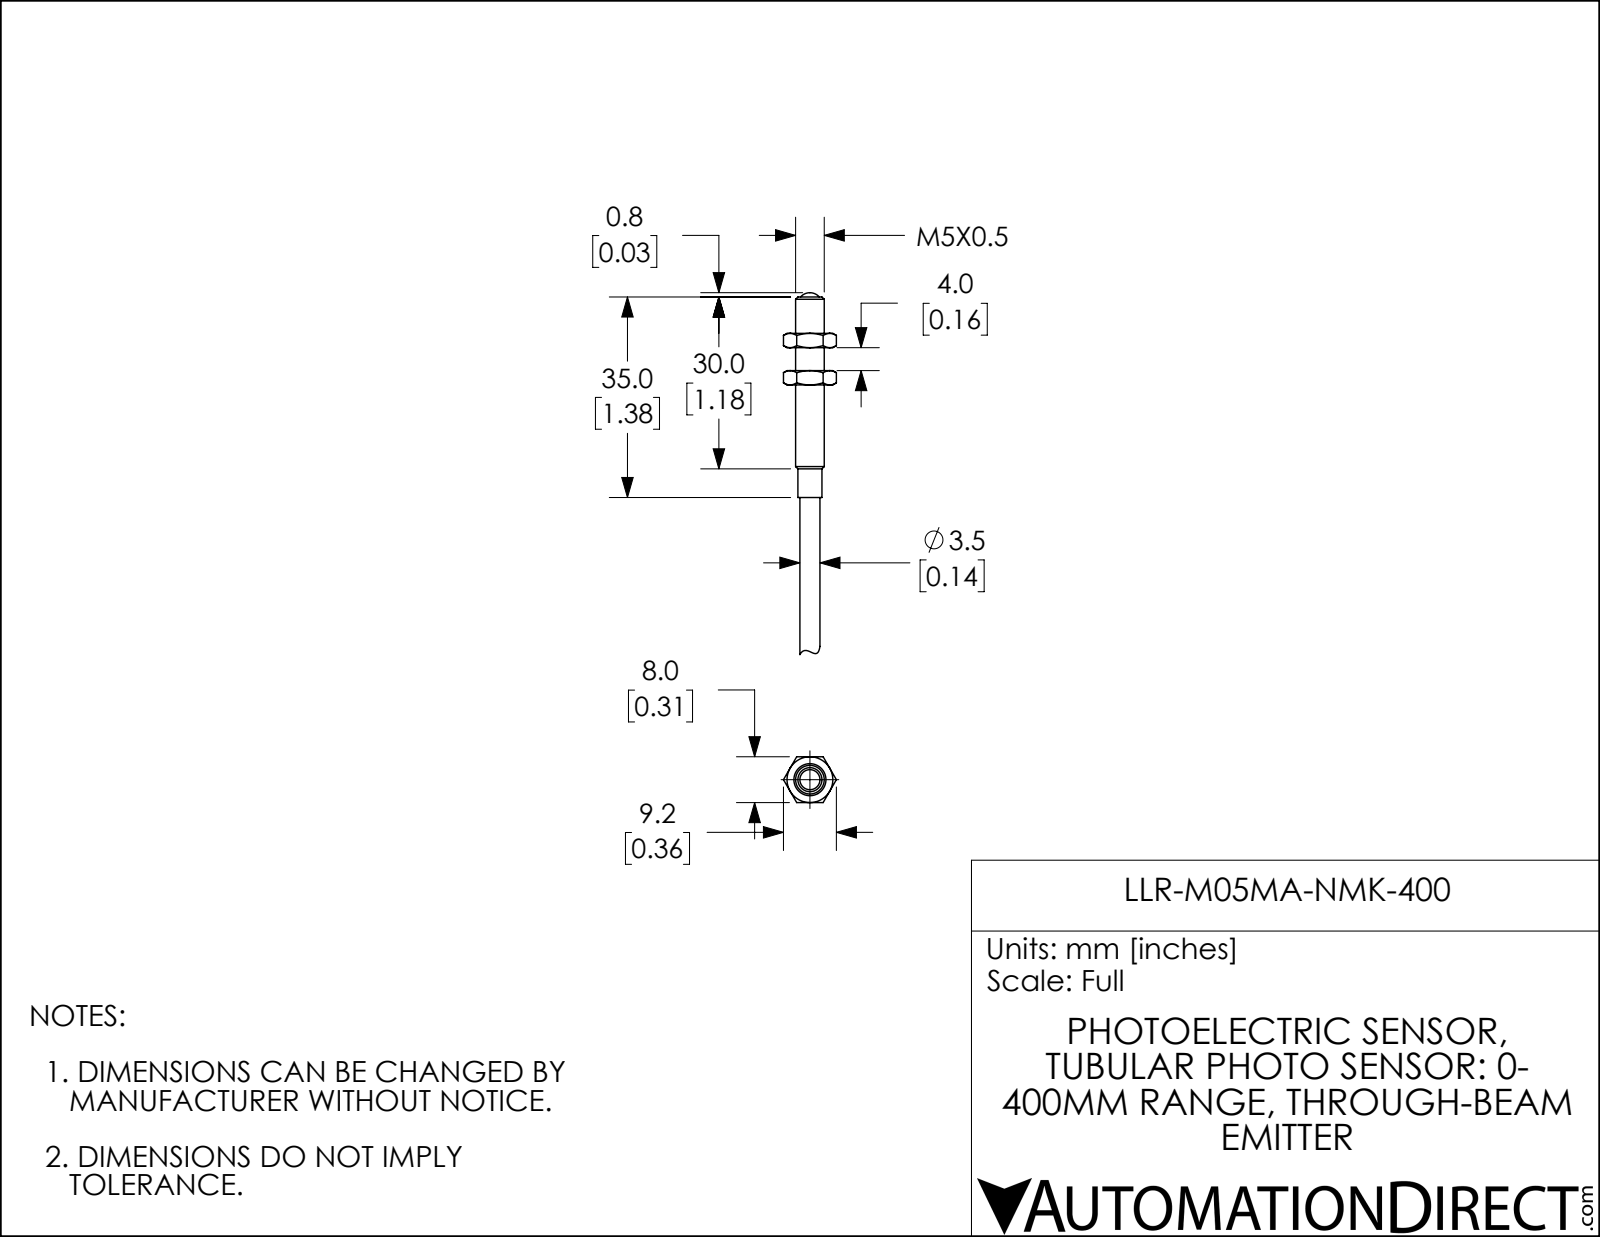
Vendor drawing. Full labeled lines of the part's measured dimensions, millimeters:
Part name (STEP PRODUCT): LLR-M05MA-NMK-400
STEP written by: SolidWorks 2018 (AUTOMOTIVE_DESIGN)
Units: millimetres
Bodies: 3 solids, 55 faces (18 planar, 5 cylindrical, 32 other)
Overall size (bounding box): 63.2 × 9.2 × 8
Volume: 1 100 mm³ · Surface area: 1 208 mm²
Round holes (diameter × count): ⌀5 ×1
Round bosses / shafts (diameter × count): ⌀4.2 ×1, ⌀3.5 ×1
Main face-to-face distances: 8, 6.5, 2.5, 4, 9, 15.3, 12.9, 8.8, 6.4, 19.7
